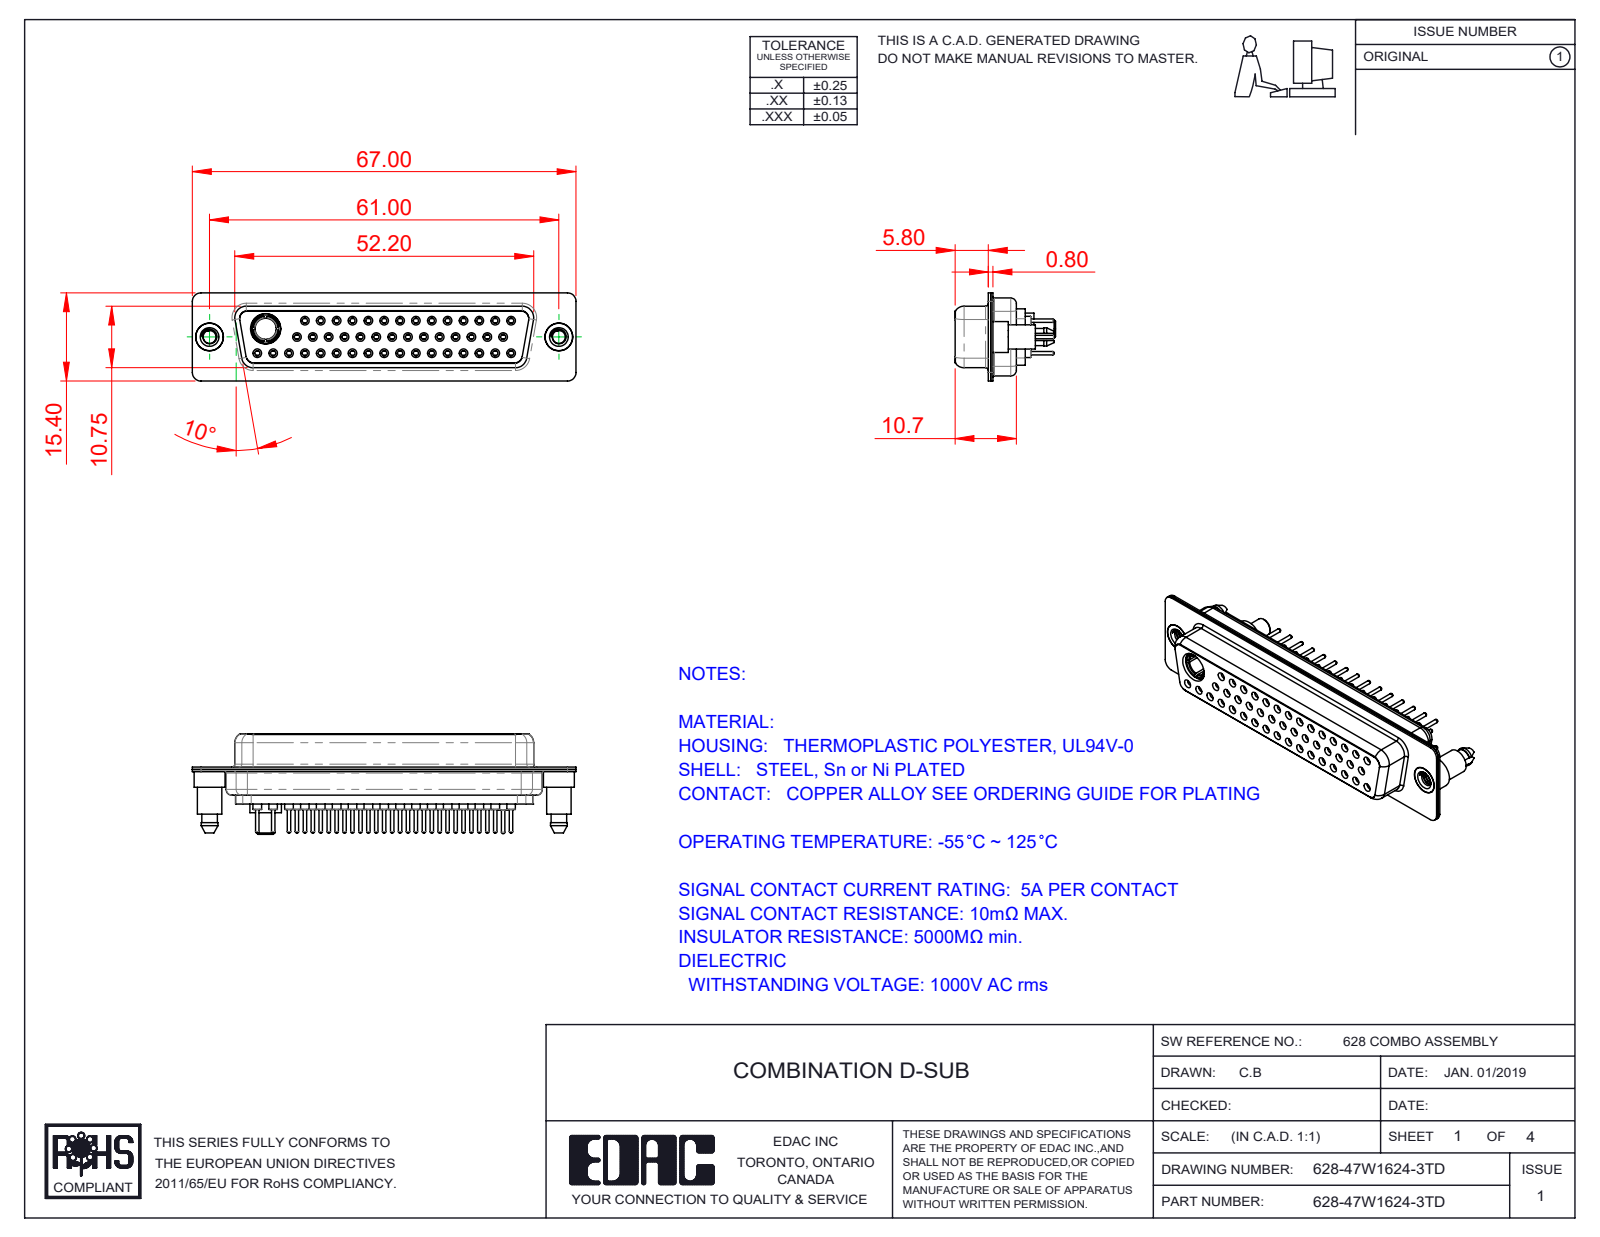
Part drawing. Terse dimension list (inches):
name: Power Socket_30A S; 628Combo Shell Front_50 Contacts; 628Combo Contact Row 1_24; 628Combo Shell Rear_50 Contacts (+5 more)
written by: SolidWorks 2016 (CONFIG_CONTROL_DESIGN)
unit: in
bodies: 53 solids, 2937 faces (799 planar, 1074 cylindrical, 1064 other)
size: 2.638 × 0.691 × 0.606
volume: 0.441 in³; area: 23.3 in²
holes: 46× ⌀0.043, 45× ⌀0.035, 45× ⌀0.059, 45× ⌀0.079, 31× ⌀0.063, 14× ⌀0.067, 3× ⌀0.191, 2× ⌀0.089, 2× ⌀0.157, 2× ⌀0.159, 1× ⌀0.146, 1× ⌀0.209
bosses: 46× ⌀0.087, 46× ⌀0.024, 15× ⌀0.063, 2× ⌀0.213, 2× ⌀0.195, 2× ⌀0.189, 2× ⌀0.167, 1× ⌀0.217
rounds: 18× R0.059, 12× R0.053, 12× R0.079, 10× R0.063, 4× R0.01, 4× R0.02, 4× R0.024, 4× R0.026
face distances: 0.016, 0.446, 0.254, 0.238, 0.074, 0.482, 0.244, 0.228, 0.407, 0.43
hole spacings: 0.124, 0.109, 0.218, 0.327, 0.436, 0.545, 0.654, 0.763
